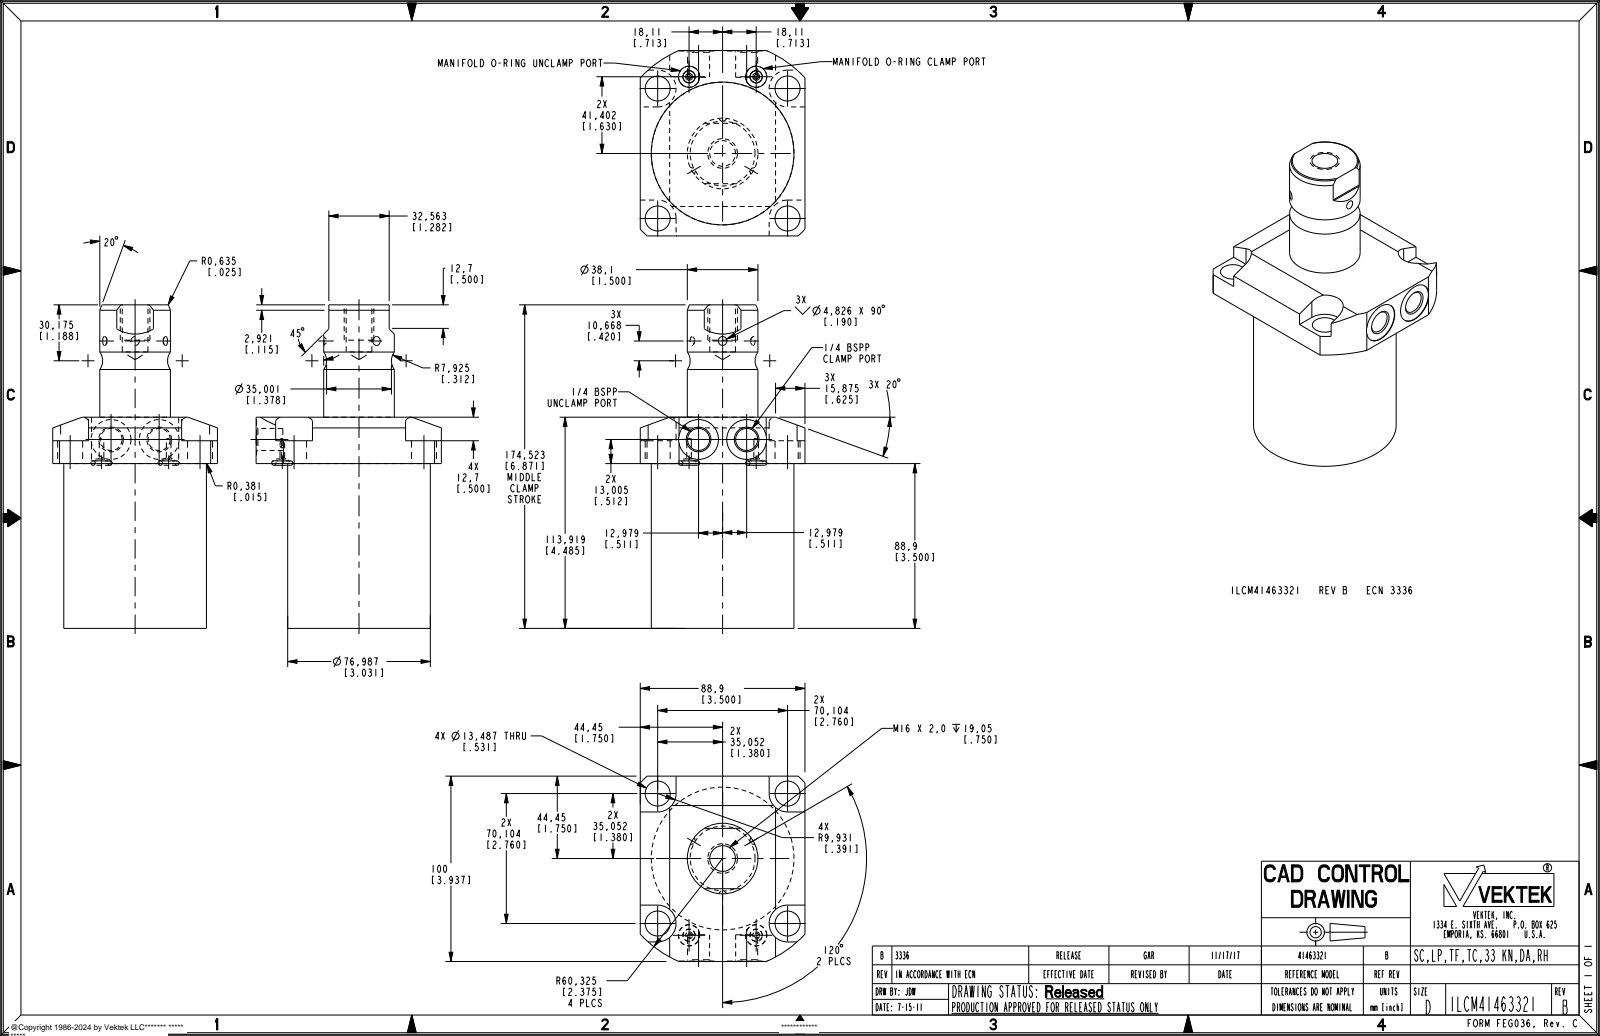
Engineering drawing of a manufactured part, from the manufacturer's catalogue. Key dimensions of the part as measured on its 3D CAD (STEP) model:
Part name (STEP PRODUCT): ILCM41463321
STEP written by: PRO/ENGINEER BY PARAMETRIC TECHNOLOGY CORPORATION, 2013320 (AUTOMOTIVE_DESIGN)
Units: millimetres
Bodies: 3 solids, 120 faces (40 planar, 48 cylindrical, 32 other)
Overall size (bounding box): 174.52 × 100 × 88.9
Volume: 657 140 mm³ · Surface area: 58 955 mm²
Round holes (diameter × count): ⌀13.49 ×4, ⌀2.49 ×2, ⌀6.5 ×2, ⌀11.4 ×2, ⌀11.89 ×2, ⌀21.49 ×2, ⌀13.87 ×1
Round bosses / shafts (diameter × count): ⌀76.99 ×1, ⌀38.1 ×1, ⌀16 ×1
Partial cylindrical surfaces — rounded edges, fillets, slot ends (radius × count): R9.93 ×4, R0.7 ×2, R60.33 ×1
Main face-to-face distances: 88.9, 113.92, 25.02, 174.52, 85.62, 60.6, 101.22, 12.32, 12.7, 73.3
Hole centre spacings: 49.57, 70.1, 18.09, 45.19, 53.54, 78.3, 93.12, 99.14
